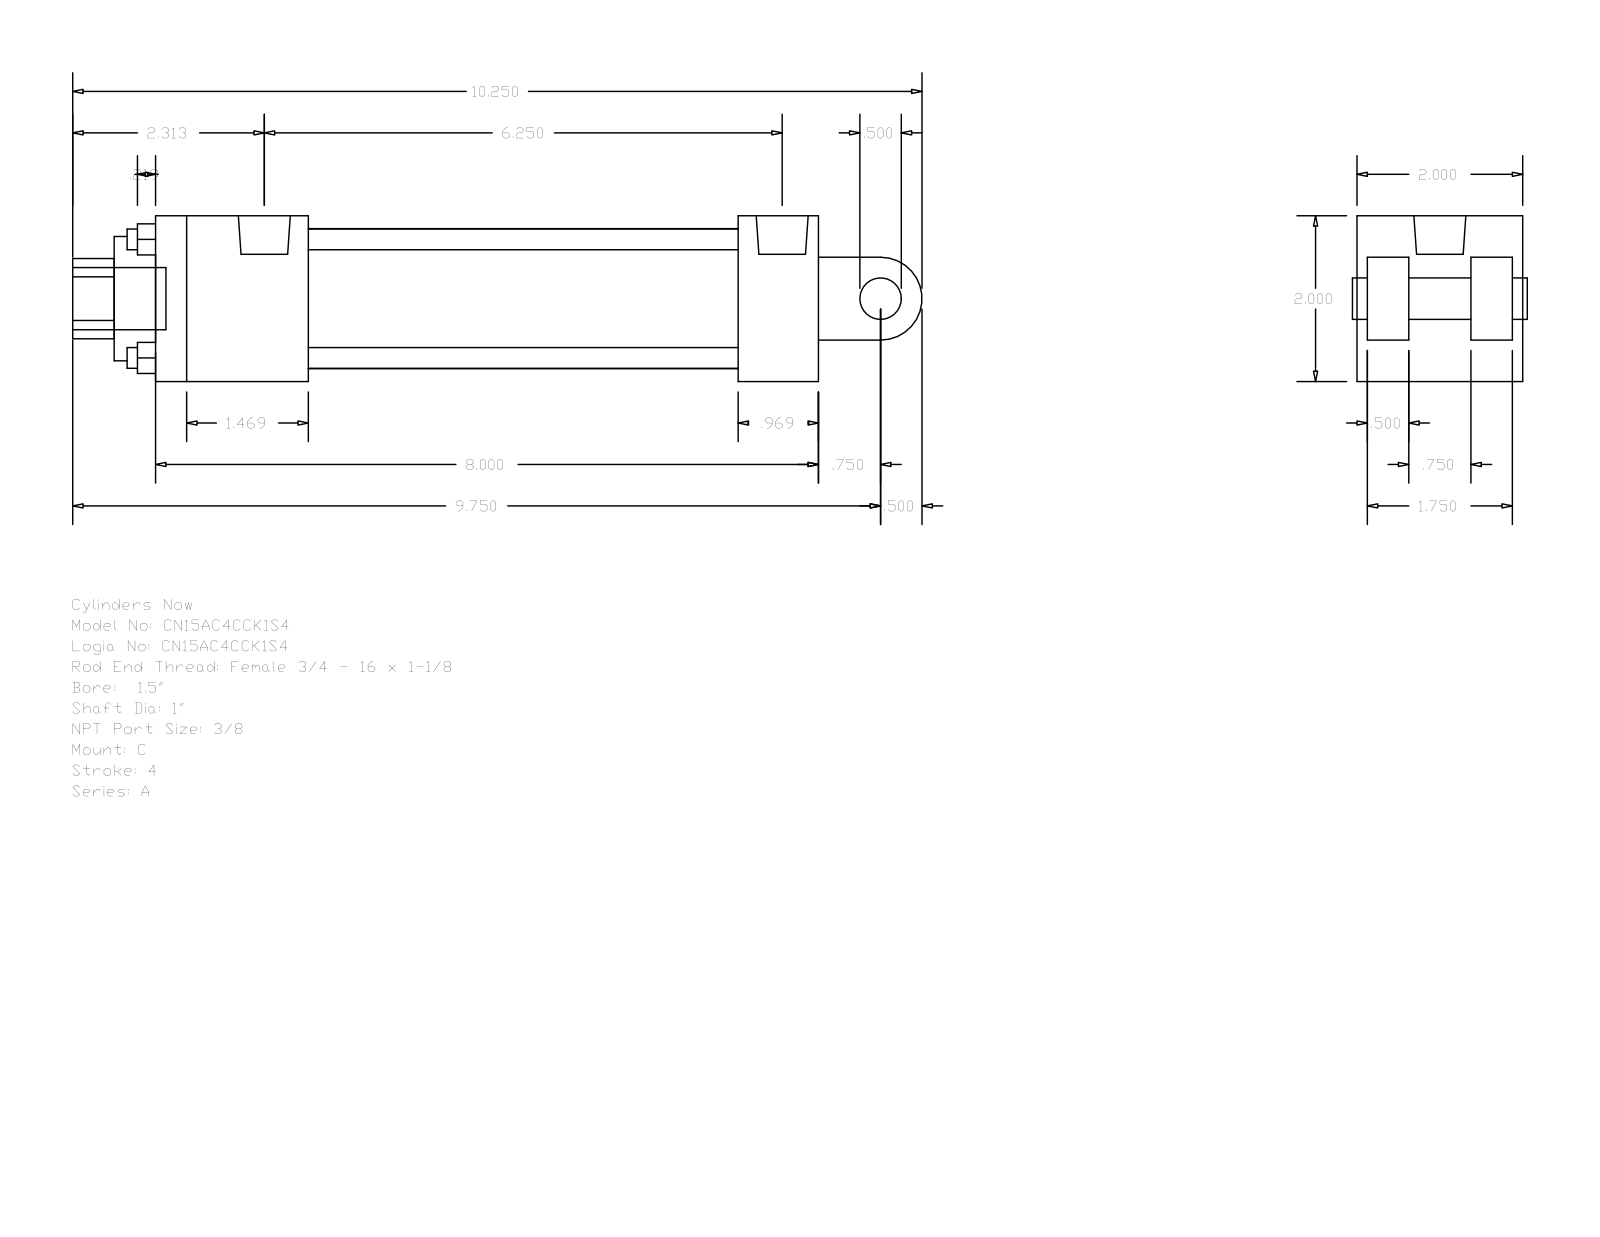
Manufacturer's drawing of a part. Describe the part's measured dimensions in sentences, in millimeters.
The part is named "A_C__0150_1". Its 3-D file was written by "GSSL Pune (CONFIG_CONTROL_DESIGN)". It is 0 solids with 99 faces: 70 planar, 29 cylindrical and 0 other. Overall it measures 260.35 by 50.8 by 50.8 millimeters. Round holes: 4 of diameter 6.35, 2 of diameter 5.56, 1 of diameter 15.93, 1 of diameter 25.4, 1 of diameter 38.1, 1 of diameter 42.93. Round bosses or shafts: 2 of diameter 5.56, 1 of diameter 19.05, 1 of diameter 15.93, 1 of diameter 12.7. Partial cylindrical surfaces (rounded edges, fillets, slot ends): 1 of radius 12.29, 1 of radius 12.7. The main face-to-face distances are 50.8, 12.7, 3.17, 15.87, 47.63, 34.93, 31.76, 203.2, 178.59, 24.61. The hole center spacings are 25.68, 36.32, 51.36, 3.97.
